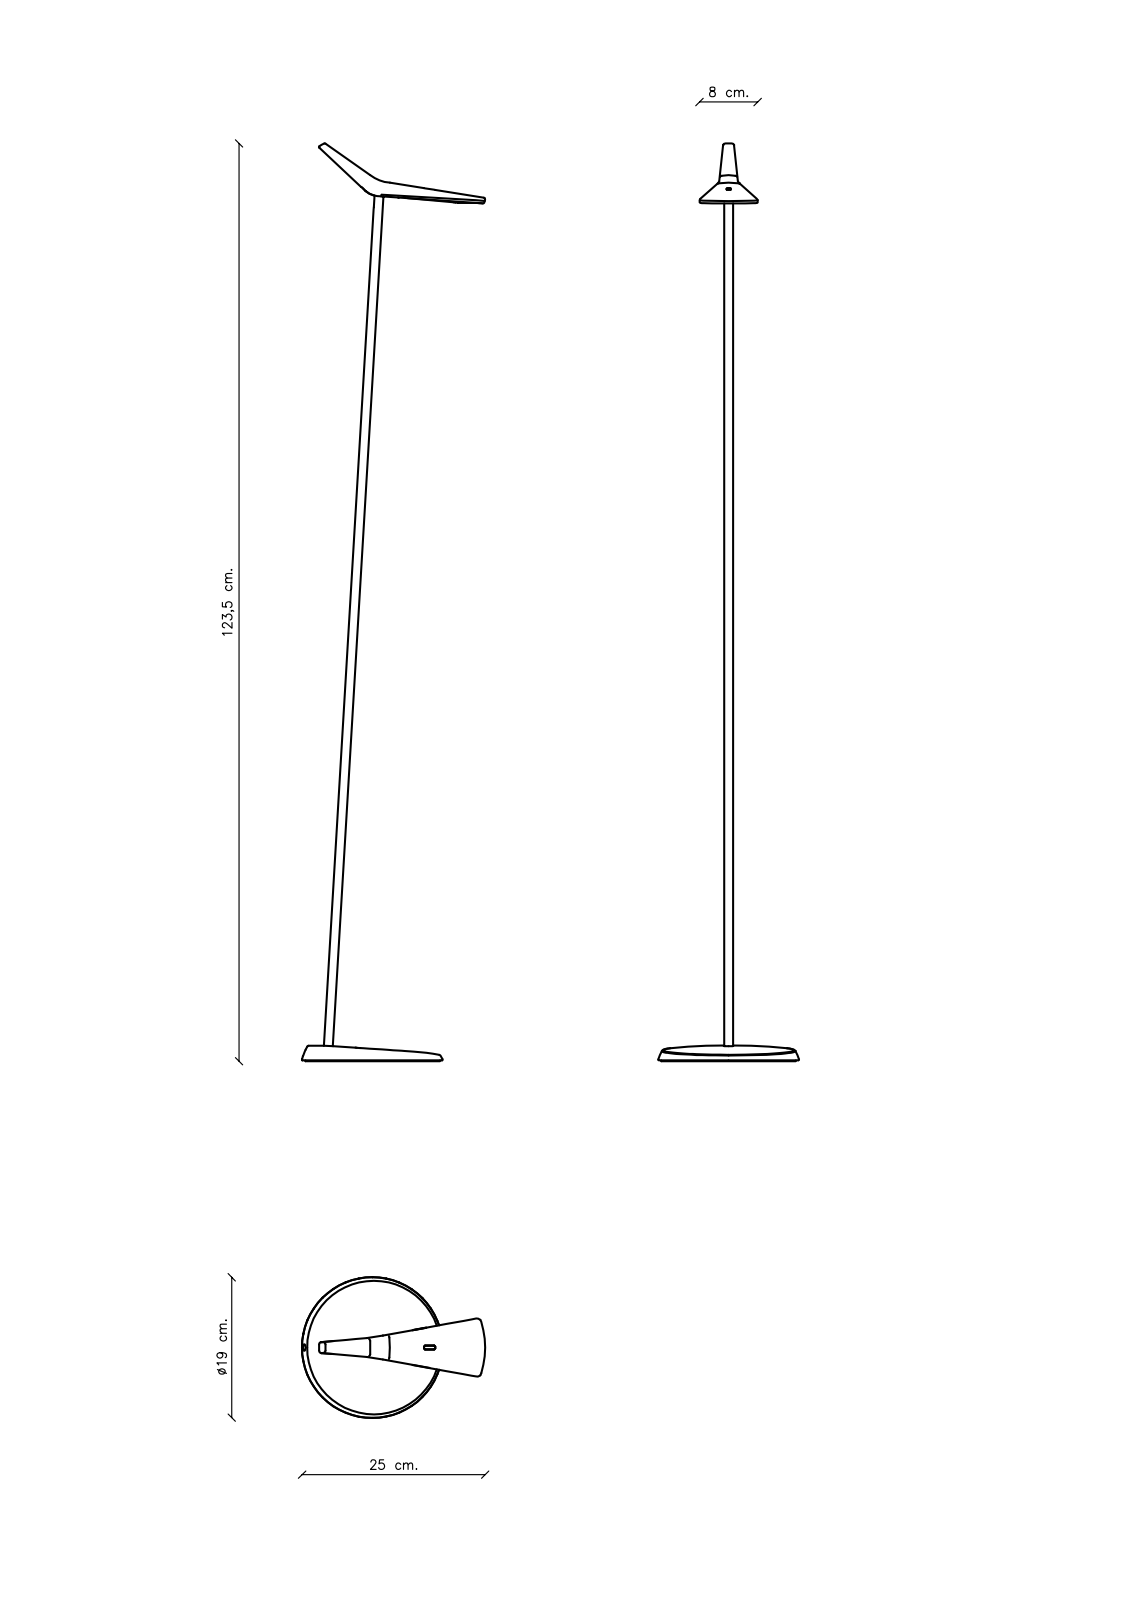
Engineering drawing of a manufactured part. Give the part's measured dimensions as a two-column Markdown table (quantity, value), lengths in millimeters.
| quantity | value |
| --- | --- |
| part name | floron; 5613828; soporte empotrar skan; chapa central sop emp skan (+7 more) |
| STEP written by | Unknown (AUTOMOTIVE_DESIGN) |
| units | millimeters |
| bodies | 71 solids, 2366 faces (1475 planar, 571 cylindrical, 320 other) |
| overall size | 1098.5 × 600 × 600 |
| volume | 3 637 000 mm³ |
| surface area | 3 189 000 mm² |
| round holes (diameter × count) | 5 × 16, 4.13 × 7, 5.1 × 7, 3 × 4, 3.2 × 4, 5.2 × 3, 15 × 3, 2.46 × 2, 3.25 × 2, 1.5 × 1, 4.4 × 1, 6 × 1 |
| round bosses / shafts (diameter × count) | 8.8 × 7, 5 × 7, 7 × 2, 585 × 1, 185 × 1, 174 × 1, 170 × 1, 162.4 × 1 |
| partial cylindrical surfaces (radius × count) | 1 × 22, 2 × 22, 0.8 × 16, 4 × 12, 1 × 8, 10.04 × 8, 11.23 × 8, 0.4 × 4 |
| main face-to-face distances | 1.5, 1, 938.45, 22, 960.45, 549, 550, 2, 23.5, 961.95 |
| hole center spacings | 70, 41.34, 121.24, 35, 59.41, 62.49, 83.21, 98.99 |
